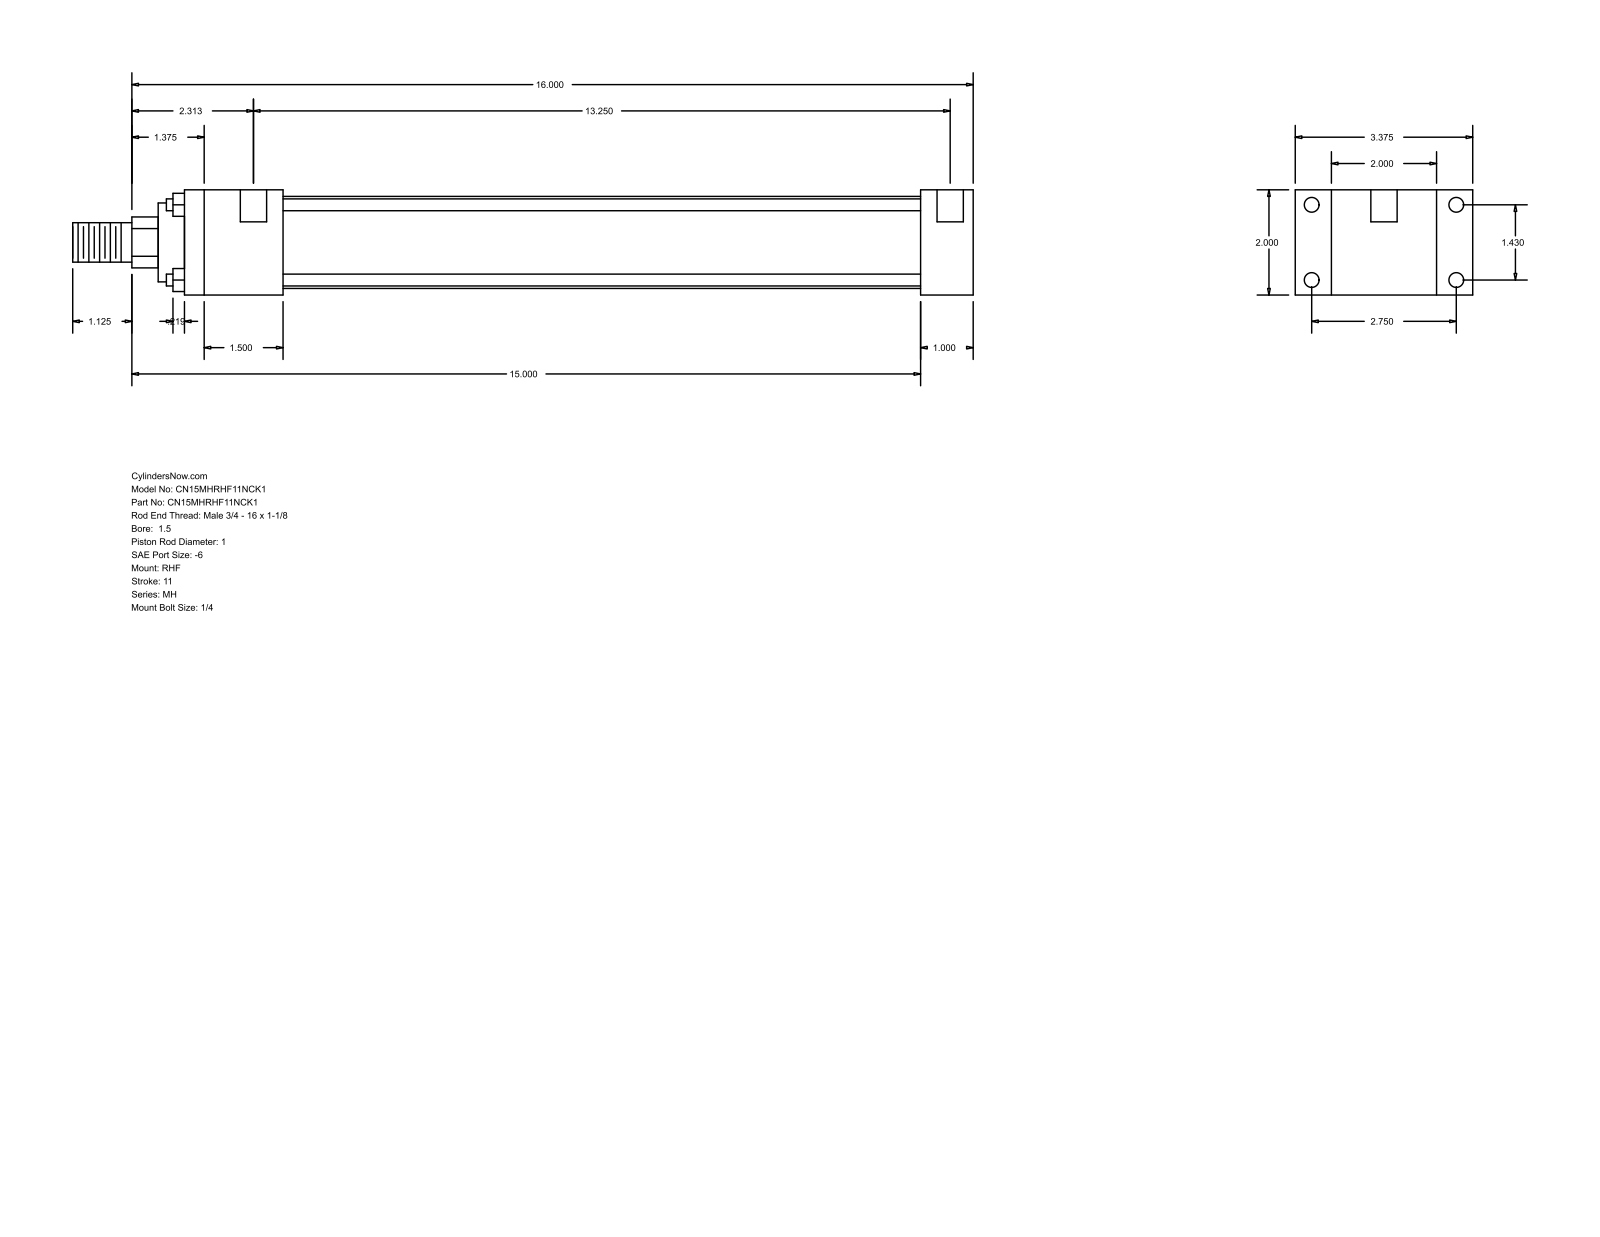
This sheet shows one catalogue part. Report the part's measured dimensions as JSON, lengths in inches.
{"part_name": "MH_RHF__0150_1", "step_written_by": "GSSL Pune (CONFIG_CONTROL_DESIGN)", "units": "inches", "bodies": {"solids": 0, "faces": 88, "planar": 60, "cylindrical": 28, "other": 0}, "overall_size": [17.125, 3.375, 2], "round_holes": [[0.219, 4], [0.281, 4], [0.5, 2]], "round_bosses_or_shafts": [[0.225, 4], [1.75, 1], [1.5, 1], [1, 1], [0.75, 1]], "partial_cylinders_radius": [[0.484, 1]], "face_to_face_distances": [2, 1, 0.687, 2.687, 3.375, 15, 14, 1.875, 12.125, 13.125], "hole_center_spacings": [1.43, 2.75, 3.099, 13.375, 0.125, 13.25]}
